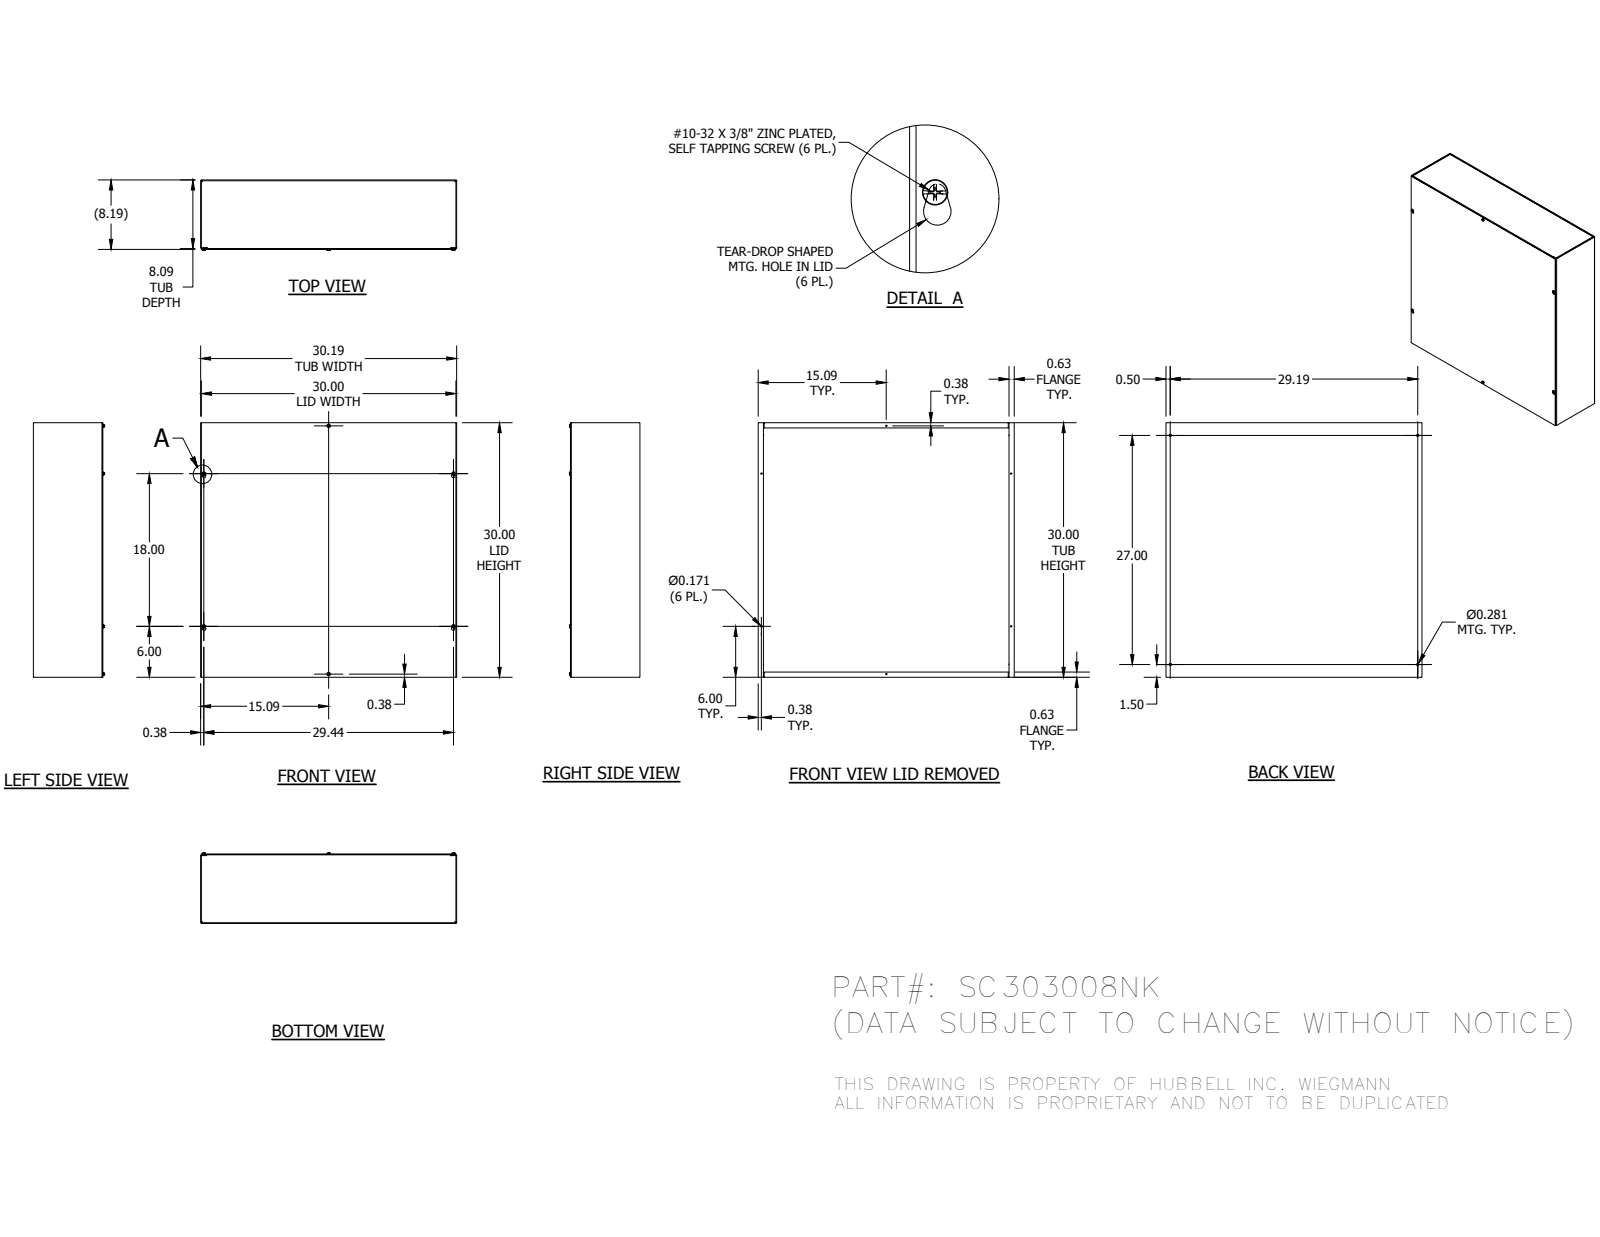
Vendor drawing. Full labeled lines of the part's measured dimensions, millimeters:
Part name (STEP PRODUCT): SC303008NKBLR; SC3008NKTB; SC3030LPA; 37214 (+1 more)
STEP written by: Autodesk Inventor 2014 (AUTOMOTIVE_DESIGN)
Units: millimetres
Bodies: 10 solids, 404 faces (232 planar, 50 cylindrical, 122 other)
Overall size (bounding box): 766.76 × 762 × 211.31
Volume: 4 407 000 mm³ · Surface area: 3 730 000 mm²
Round holes (diameter × count): ⌀4.34 ×6, ⌀7.14 ×4, ⌀7.92 ×2
Round bosses / shafts (diameter × count): ⌀4.83 ×6
Partial cylindrical surfaces — rounded edges, fillets, slot ends (radius × count): R0.4 ×12, R2.78 ×12, R3.17 ×4, R5.16 ×4
Main face-to-face distances: 2.38, 205.58, 203.2, 207.96, 762, 759.62, 764.38, 757.24, 766.76, 4.76
Hole centre spacings: 114.34, 371.78, 400.23, 571.51, 707, 753.26, 804.82, 938.59
